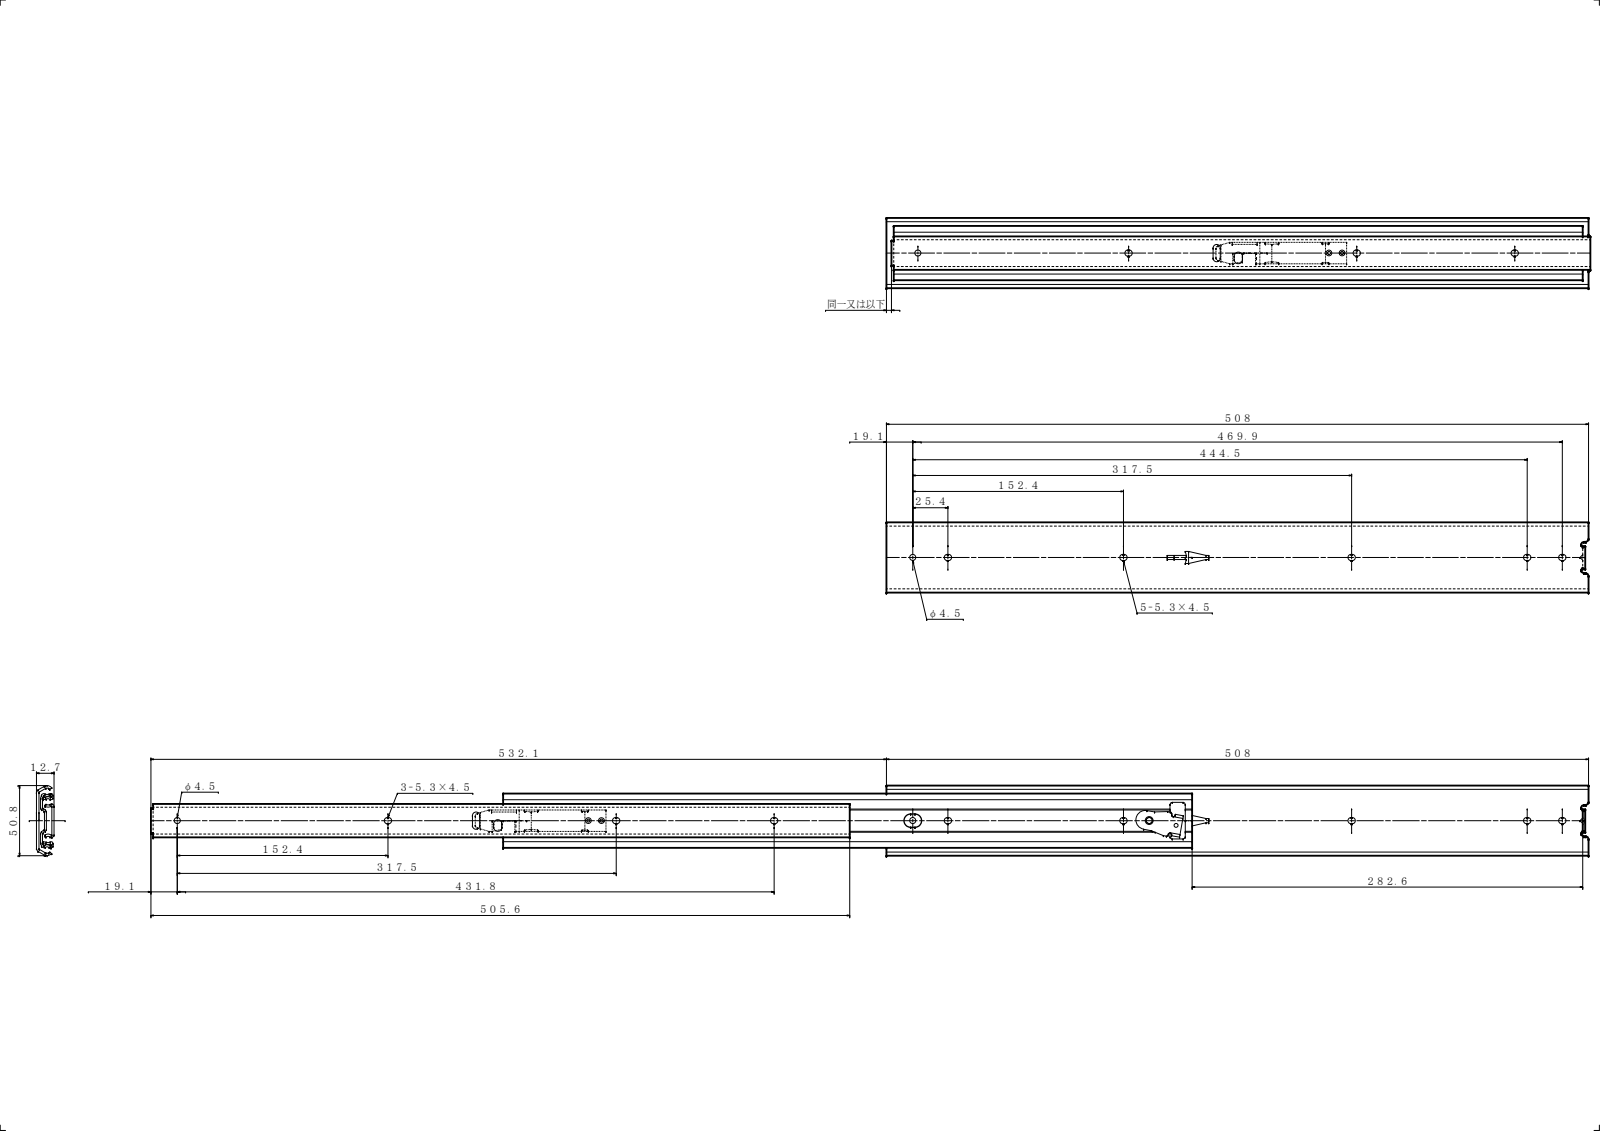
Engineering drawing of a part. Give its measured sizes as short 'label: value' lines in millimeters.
name: Y515_20 CM; フリッパーロックKB09; Y515_20 OM; Y515_20 IM (+4 more)
written by: SolidWorks 2019 (CONFIG_CONTROL_DESIGN)
unit: mm
bodies: 9 solids, 334 faces (166 planar, 162 cylindrical, 6 other)
size: 1040.1 × 50.8 × 12.7
volume: 138 151 mm³; area: 180 203 mm²
holes: 3× ⌀4.5, 2× ⌀2.4, 2× ⌀2.8, 2× ⌀4.2, 1× ⌀3, 1× ⌀5.9
bosses: 2× ⌀2.3, 1× ⌀10, 1× ⌀5.8, 1× ⌀4.4
rounds: 16× R2.25, 12× R1.5, 12× R2, 9× R0.5, 7× R1, 4× R0.4, 4× R0.8, 4× R1.27
face distances: 1.8, 1.4, 3.95, 5.35, 2.75, 9.3, 11.1, 1.6, 12.7, 10.9
hole spacings: 7.5, 230.02, 302.21, 401.09, 421.09, 9.5, 11.6, 20
